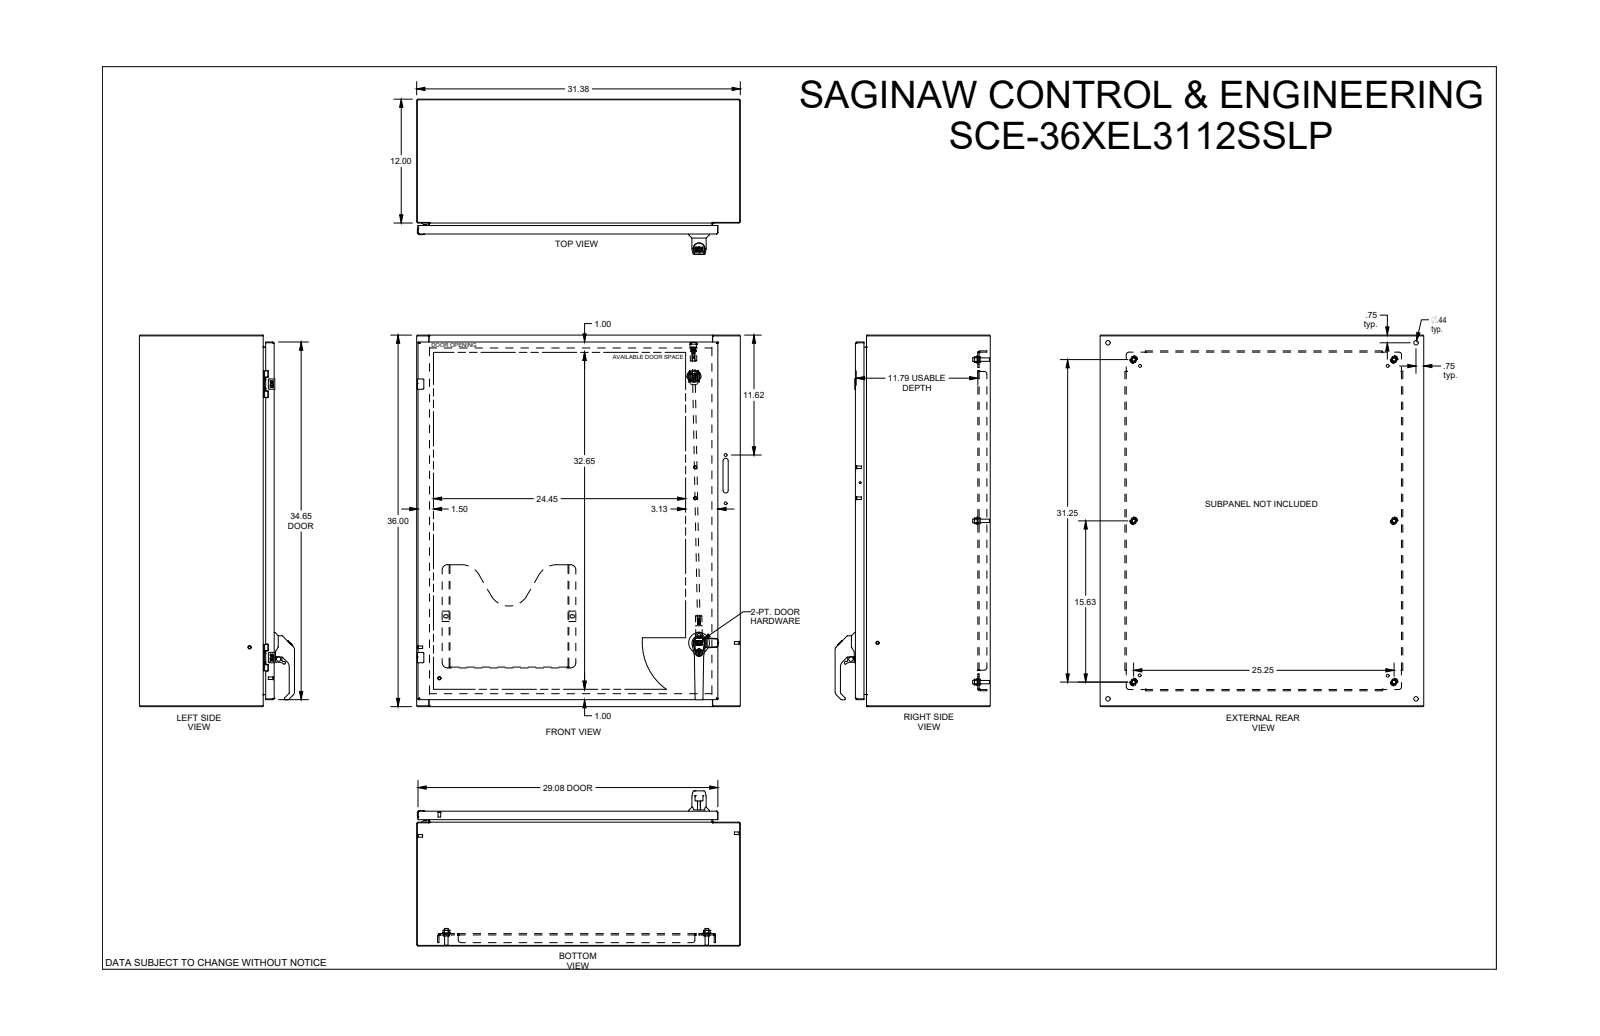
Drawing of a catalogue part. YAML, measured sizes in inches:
part_name: "SCE-36XEL3112SSLP"
step_written_by: "SolidWorks 2019 (CONFIG_CONTROL_DESIGN)"
units: inches
bodies: {solids: 71, faces: 4738, planar: 1767, cylindrical: 1238, other: 1733}
overall_size: [36, 31.375, 15.036]
volume: 473.4
surface_area: 10907
round_holes:
  - {diameter: 0.281, count: 6}
  - {diameter: 0.367, count: 6}
  - {diameter: 0.5, count: 6}
  - {diameter: 0.266, count: 5}
  - {diameter: 0.172, count: 4}
  - {diameter: 0.205, count: 4}
  - {diameter: 0.244, count: 4}
  - {diameter: 0.375, count: 4}
  - {diameter: 0.437, count: 4}
  - {diameter: 0.25, count: 3}
  - {diameter: 0.25, count: 3}
  - {diameter: 0.138, count: 2}
round_bosses_or_shafts:
  - {diameter: 0.248, count: 8}
  - {diameter: 0.366, count: 6}
  - {diameter: 0.332, count: 6}
  - {diameter: 0.17, count: 6}
  - {diameter: 0.25, count: 4}
  - {diameter: 0.563, count: 3}
  - {diameter: 0.196, count: 3}
  - {diameter: 0.341, count: 2}
partial_cylinders:
  - {radius: 0.03, count: 69}
  - {radius: 0.015, count: 54}
  - {radius: 0.01, count: 48}
  - {radius: 0.02, count: 36}
  - {radius: 0.02, count: 34}
  - {radius: 0.04, count: 31}
  - {radius: 0.039, count: 30}
  - {radius: 0.005, count: 26}
face_to_face_distances: [0.075, 12.993, 0.075, 12.918, 13.068, 1.125, 1.2, 11.868, 11.793, 0.125]
hole_center_spacings: [26.5, 0.985, 0.02, 4.493, 26.542, 26.562, 0.472, 0.725]
